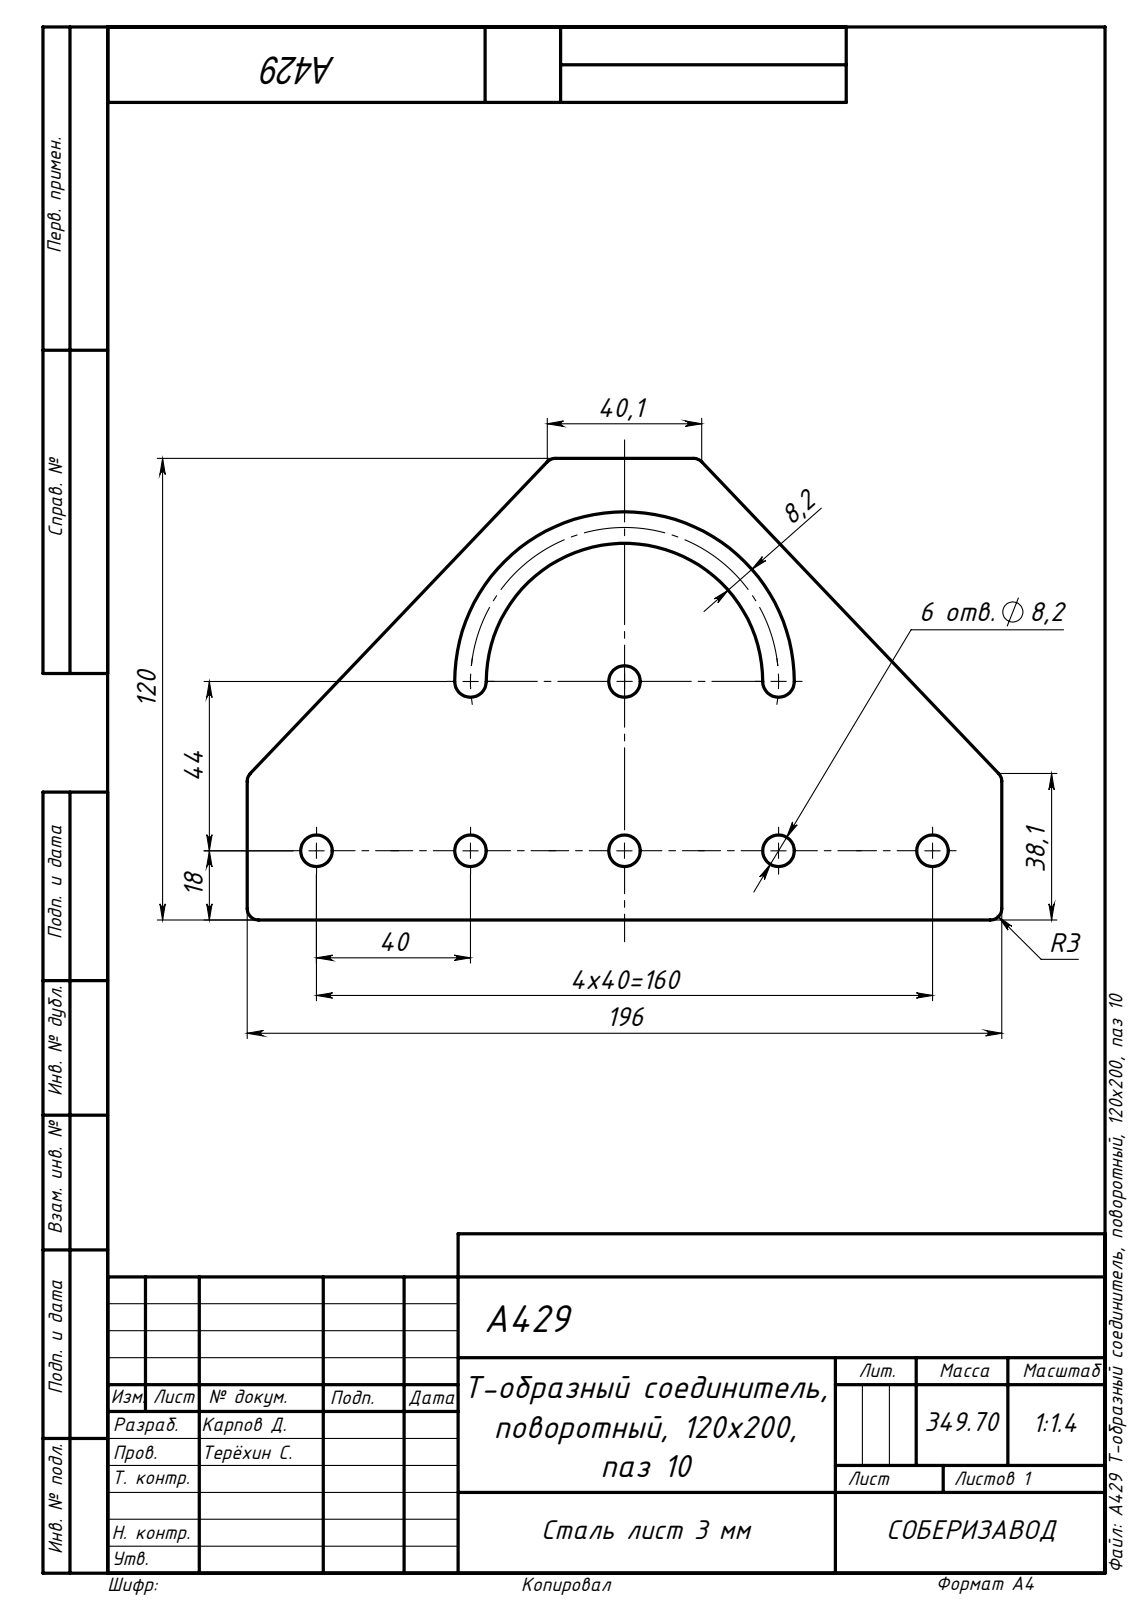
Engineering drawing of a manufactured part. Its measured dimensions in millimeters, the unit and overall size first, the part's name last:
Units: millimetres
Overall size (bounding box): 196 × 120 × 3
Round holes (diameter × count): ⌀8.2 ×6
Partial cylindrical surfaces — rounded edges, fillets, slot ends (radius × count): R3 ×6, R4.1 ×2, R35.9 ×1, R44.1 ×1
Main face-to-face distances: 3, 120, 196
Hole centre spacings: 40, 80, 59.46, 91.3, 120, 44, 160
Volume: 46 758 mm³ · Surface area: 34 070 mm²
Bodies: 1 solid, 30 faces (8 planar, 22 cylindrical, 0 other)
STEP written by: SolidWorks 2020 (AUTOMOTIVE_DESIGN)
